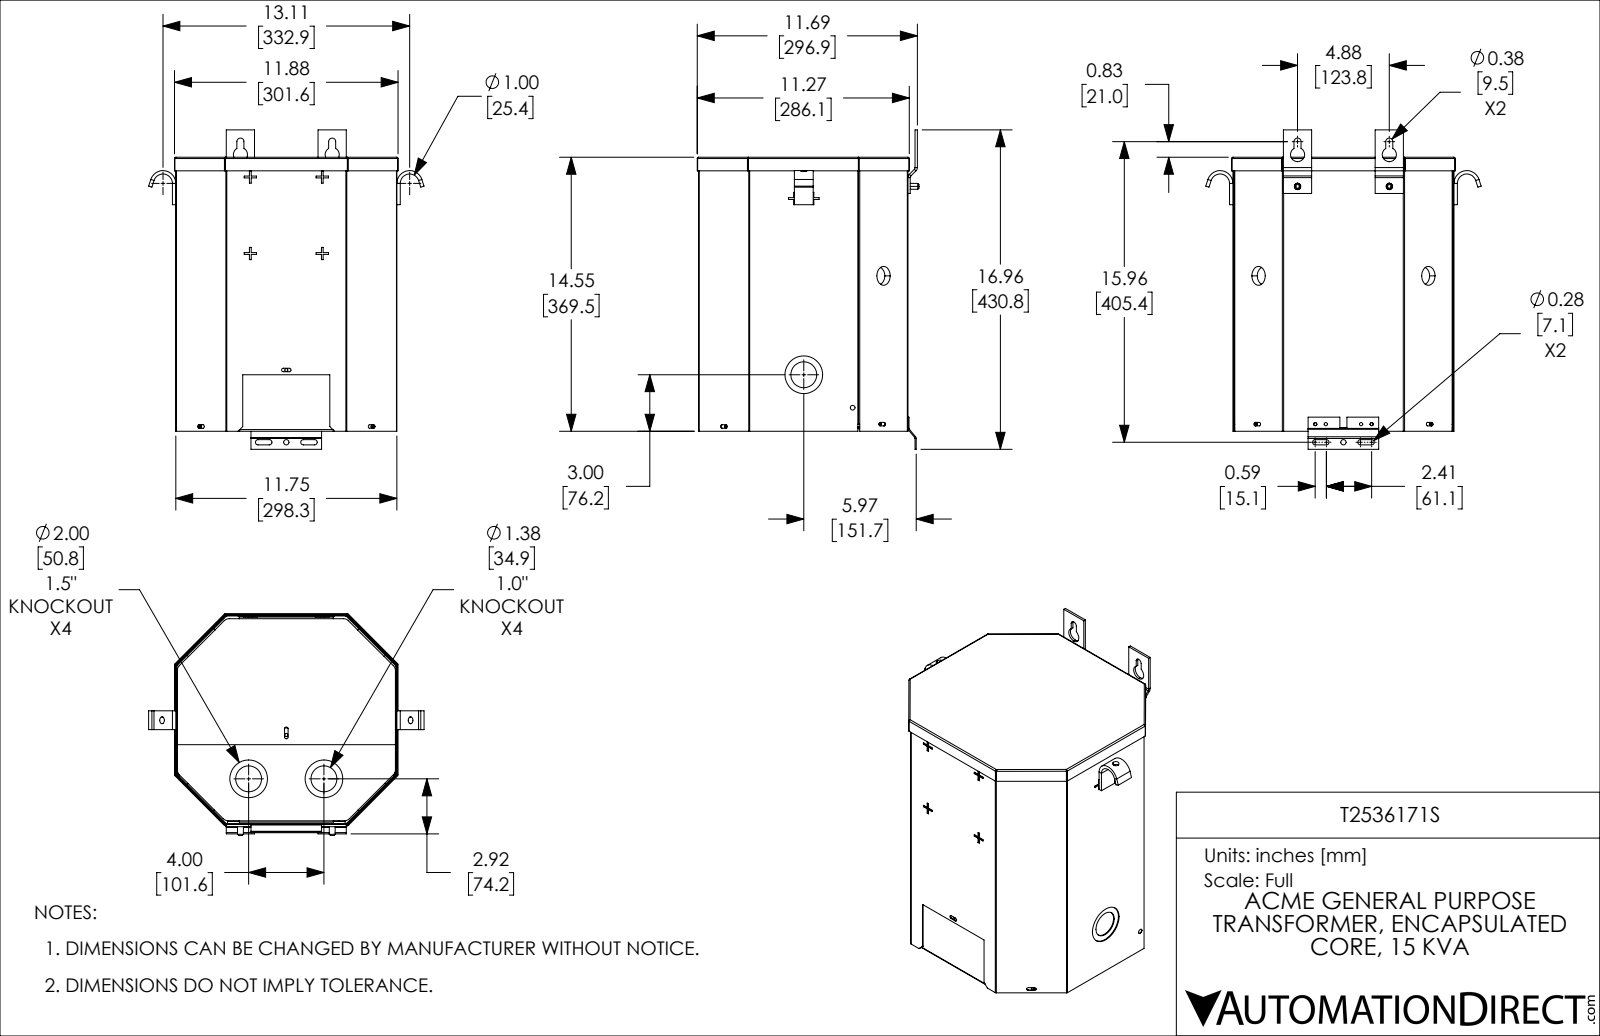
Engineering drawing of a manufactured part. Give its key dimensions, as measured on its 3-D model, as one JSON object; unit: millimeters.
{"part_name": "T2536171S", "step_written_by": "SolidWorks 2021 (CONFIG_CONTROL_DESIGN)", "units": "millimeters", "bodies": {"solids": 13, "faces": 768, "planar": 526, "cylindrical": 206, "other": 36}, "overall_size": [430.78, 371.54, 299.05], "volume_mm3": 779181, "surface_area_mm2": 1190000, "round_holes": [[4.06, 8], [4.34, 4], [50.8, 3], [6.35, 2], [6.5, 2], [7.14, 2], [7.94, 2], [8.73, 2], [19.05, 2], [34.93, 2], [4.76, 1], [34.92, 1]], "round_bosses_or_shafts": [[7.92, 2], [53.23, 1], [37.35, 1]], "partial_cylinders_radius": [[2.38, 16], [0.61, 15], [1.82, 15], [9.53, 8], [1.27, 4], [2.48, 4], [3.57, 4], [0.76, 3]], "face_to_face_distances": [1.22, 1.21, 313.48, 297.13, 281.12, 312.26, 314.7, 1.52, 364.87, 295.92], "hole_center_spacings": [327.02, 14.29, 61.91, 0.7, 17.64, 42.86, 45.23, 76.2]}
